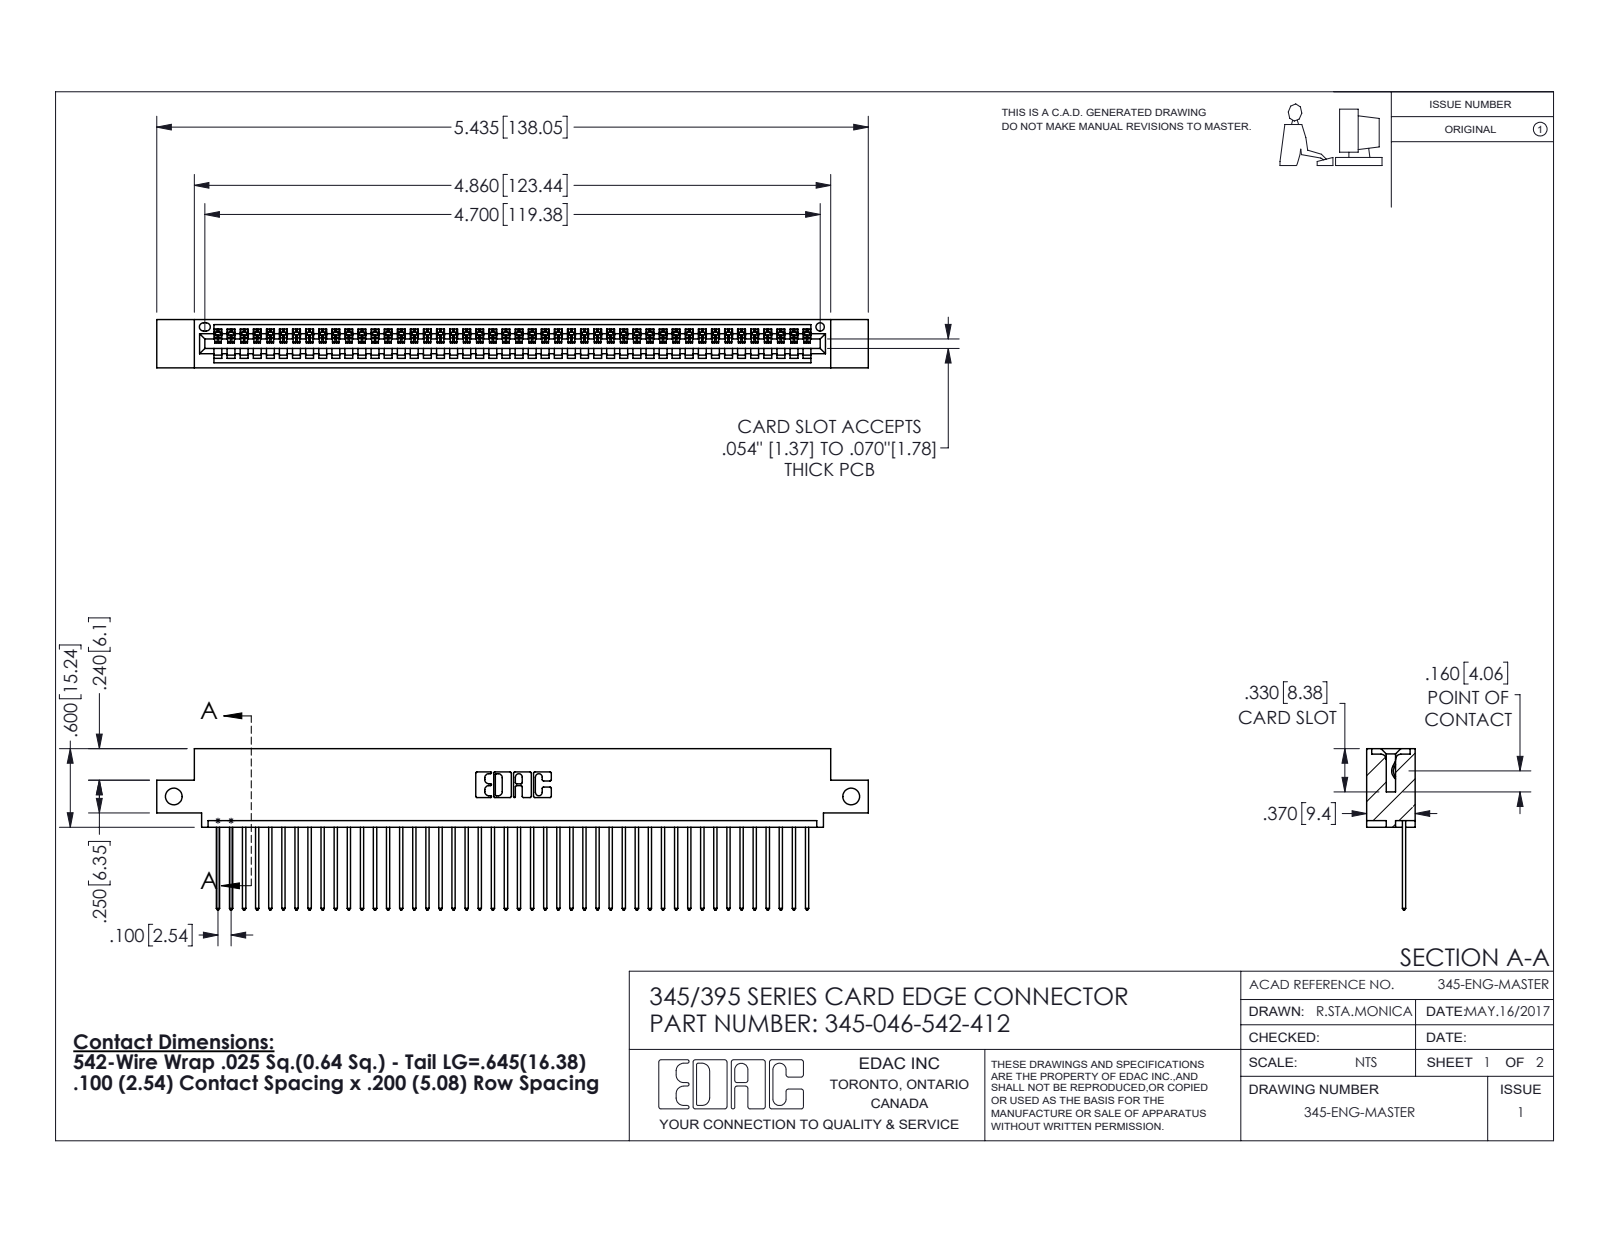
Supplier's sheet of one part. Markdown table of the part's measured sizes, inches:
| quantity | value |
| --- | --- |
| part name | 345-046-542-412; 345 Part_0.110 Offset - Side Mount; 345-292-001_345-293-142 |
| STEP written by | SolidWorks 2016 (CONFIG_CONTROL_DESIGN) |
| units | inches |
| bodies | 47 solids, 2798 faces (1924 planar, 874 cylindrical, 0 other) |
| overall size | 5.435 × 1.232 × 0.37 |
| volume | 0.799 in³ |
| surface area | 27.95 in² |
| round holes (diameter × count) | 0.128 × 2, 0.064 × 1 |
| partial cylindrical surfaces (radius × count) | 0.006 × 92, 0.01 × 92, 0.01 × 22, 0.007 × 6, 0.031 × 6, 0.026 × 3, 0.031 × 2, 0.04 × 2 |
| main face-to-face distances | 0.072, 0.298, 0.098, 0.272, 0.025, 0.37, 0.2, 0.225, 0.149, 0.072 |
| hole center spacings | 5.175 |
